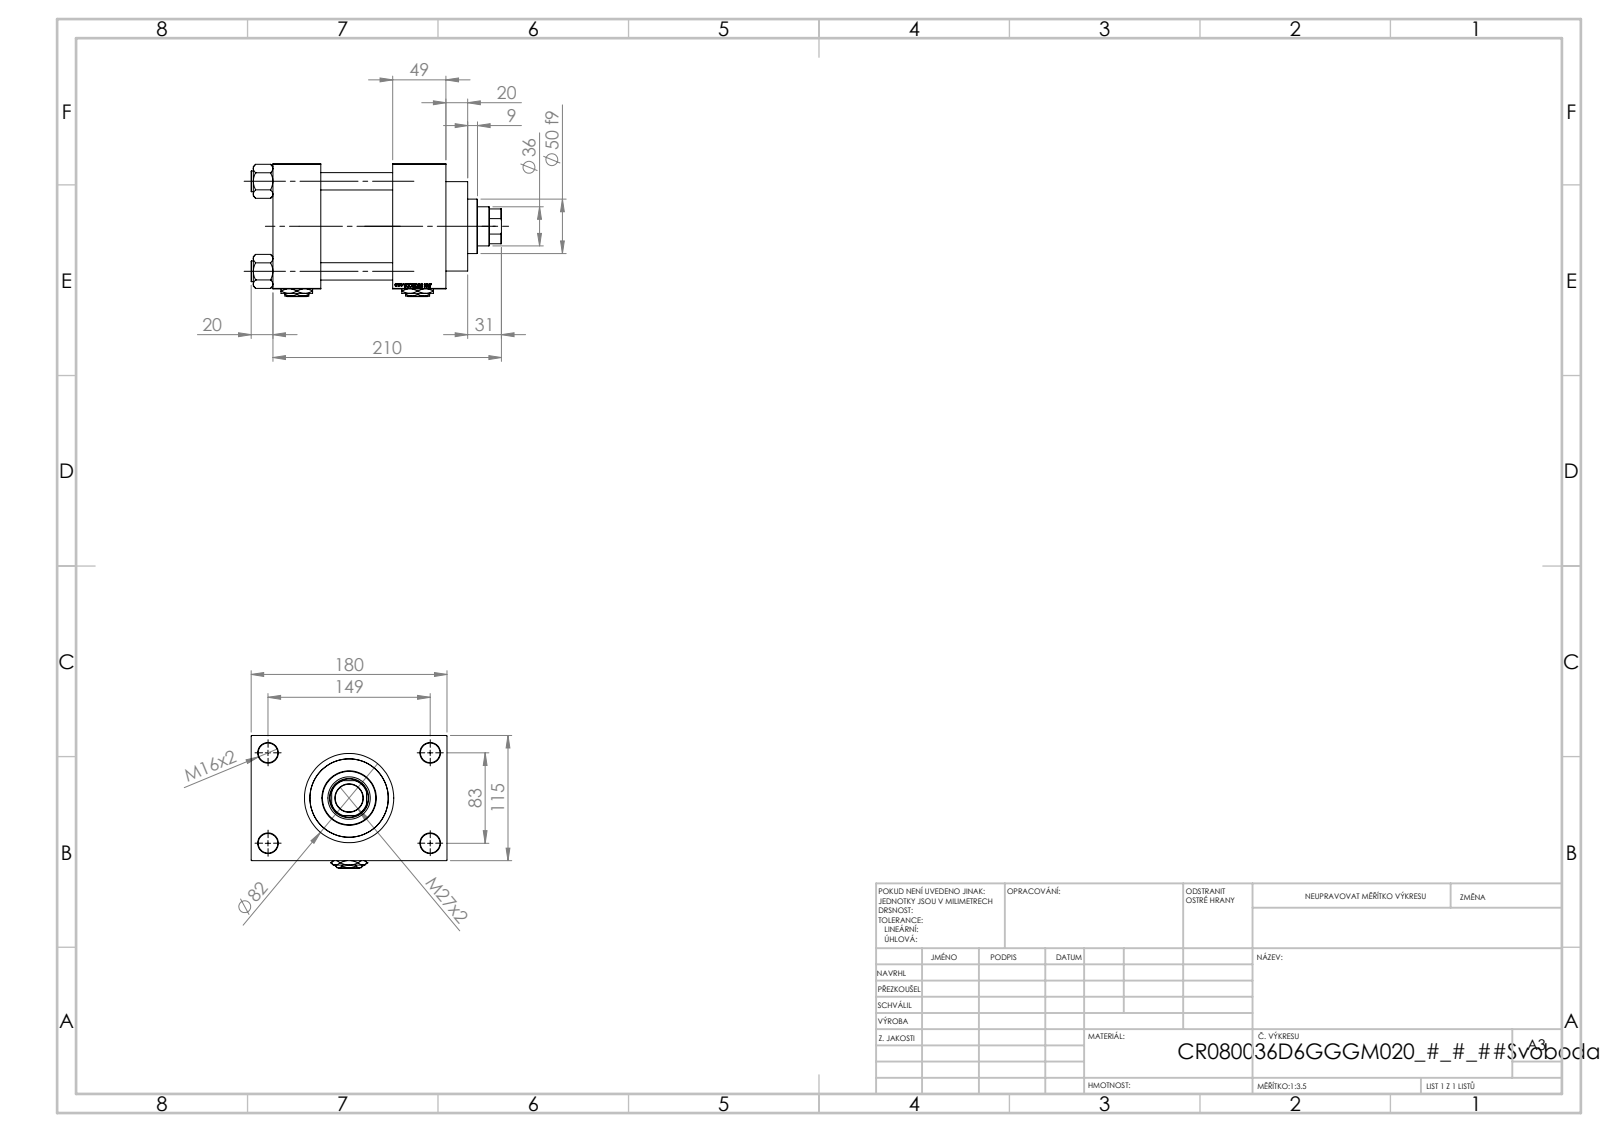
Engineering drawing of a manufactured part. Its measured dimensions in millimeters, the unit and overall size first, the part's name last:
Units: millimetres
Overall size (bounding box): 230 × 180 × 122
Round holes (diameter × count): ⌀16 ×4, ⌀18 ×4, ⌀7 ×2, ⌀26.44 ×2, ⌀35 ×2, ⌀25.5 ×1, ⌀36 ×1, ⌀39 ×1, ⌀61 ×1, ⌀72 ×1, ⌀80 ×1
Round bosses / shafts (diameter × count): ⌀19 ×4, ⌀86 ×1, ⌀82 ×1, ⌀50 ×1
Partial cylindrical surfaces — rounded edges, fillets, slot ends (radius × count): R17.5 ×1
Main face-to-face distances: 115, 66, 110, 49, 44, 159, 147.5, 32.5, 20, 69
Hole centre spacings: 33.15, 58.48, 82.7, 85.28, 89.24, 115.85, 142.43, 83
Volume: 1 983 000 mm³ · Surface area: 300 614 mm²
Bodies: 13 solids, 1253 faces (593 planar, 100 cylindrical, 560 other)
Part name (STEP PRODUCT): V215CR_D_TYCINKA; NUT_M5_D; V215_VC_A; V215CR_D_Body (+2 more)
STEP written by: SolidWorks 2019 (CONFIG_CONTROL_DESIGN)
